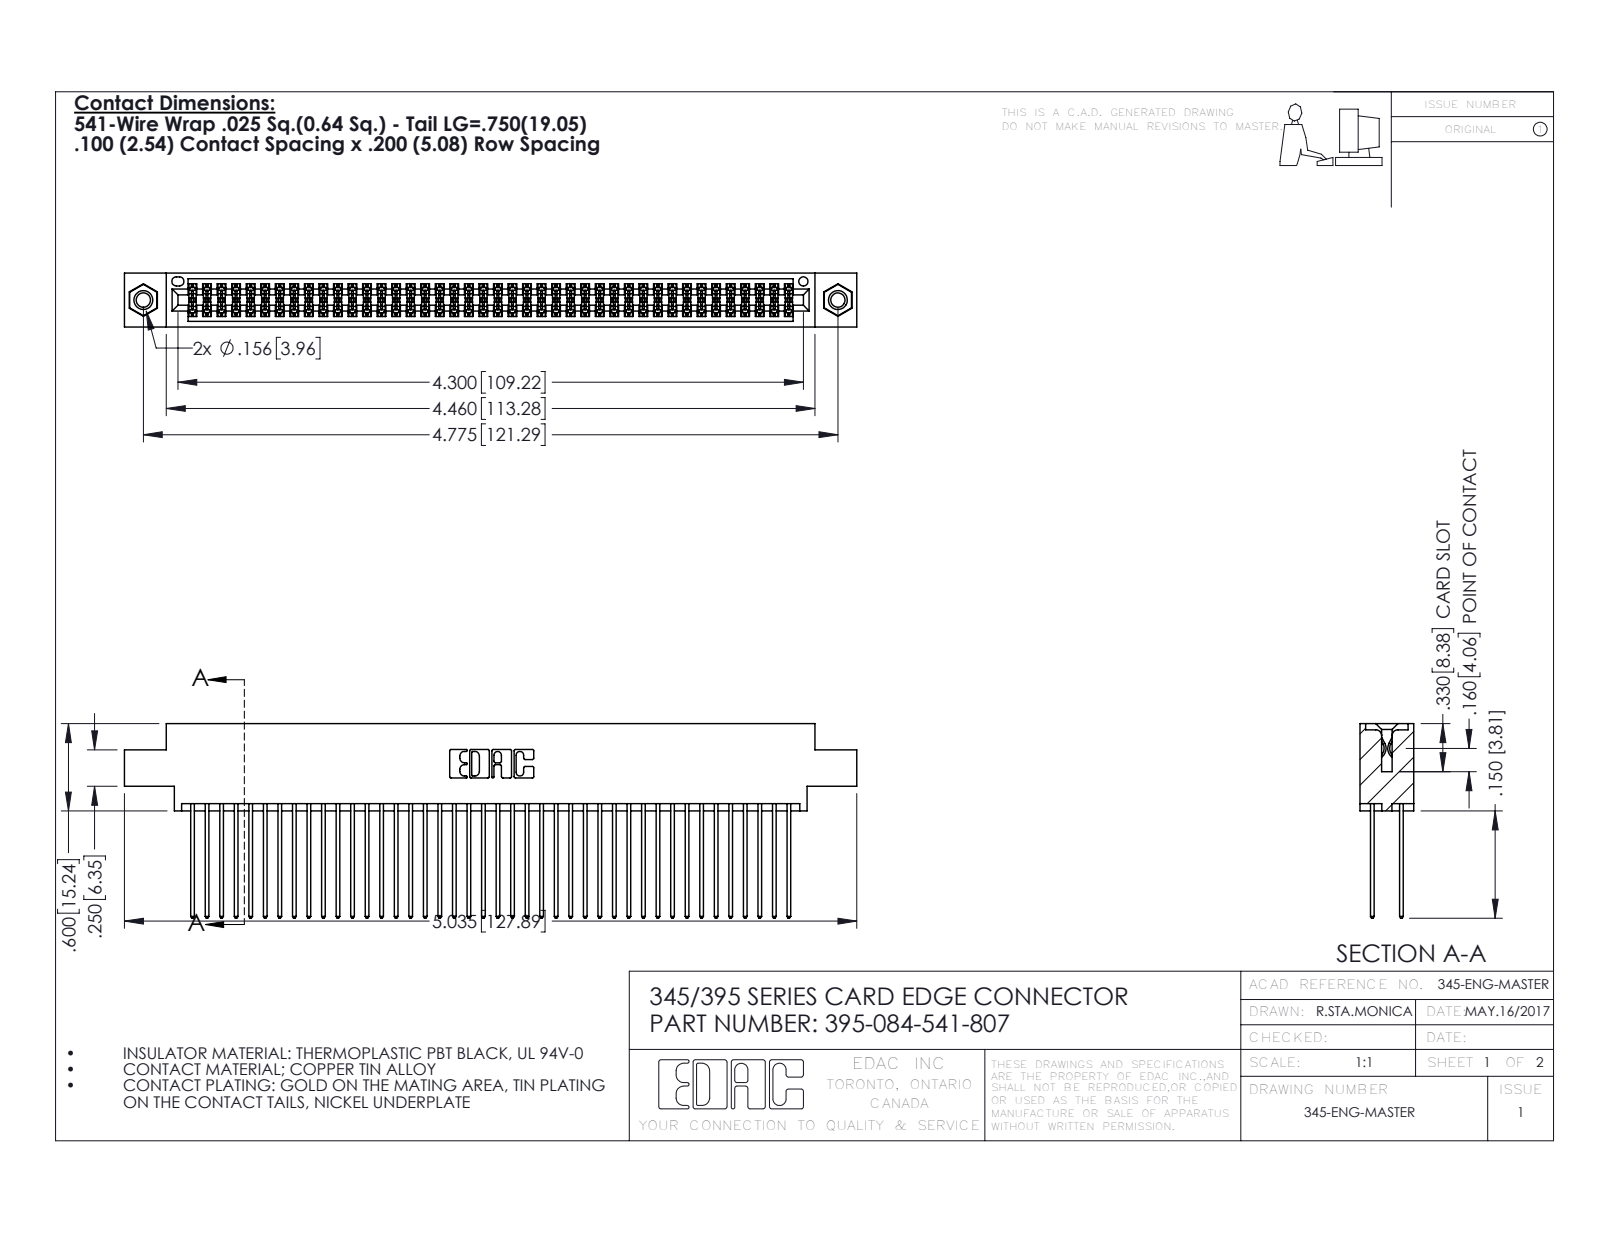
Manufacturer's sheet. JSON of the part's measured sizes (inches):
{"part_name": "345-292-001_345-293-141; 345-250-001_345-250-005-103; 395-084-541-807; 345 Part_0.170 Offset - 0.156 Dia-TI", "step_written_by": "SolidWorks 2016 (CONFIG_CONTROL_DESIGN)", "units": "inches", "bodies": {"solids": 87, "faces": 4390, "planar": 2888, "cylindrical": 1486, "other": 16}, "overall_size": [5.035, 1.337, 0.37], "volume_in3": 0.78, "surface_area_in2": 33.05, "round_holes": [[0.098, 2], [0.125, 2], [0.156, 2], [0.064, 1]], "round_bosses_or_shafts": [[0.155, 2]], "partial_cylinders_radius": [[0.006, 126], [0.01, 84], [0.01, 22], [0.007, 6], [0.031, 6], [0.026, 3], [0.014, 2], [0.019, 2]], "face_to_face_distances": [0.072, 0.298, 0.2, 0.098, 0.272, 0.025, 0.37, 0.225, 0.175, 0.149], "hole_center_spacings": [0.27, 4.539, 4.775]}
